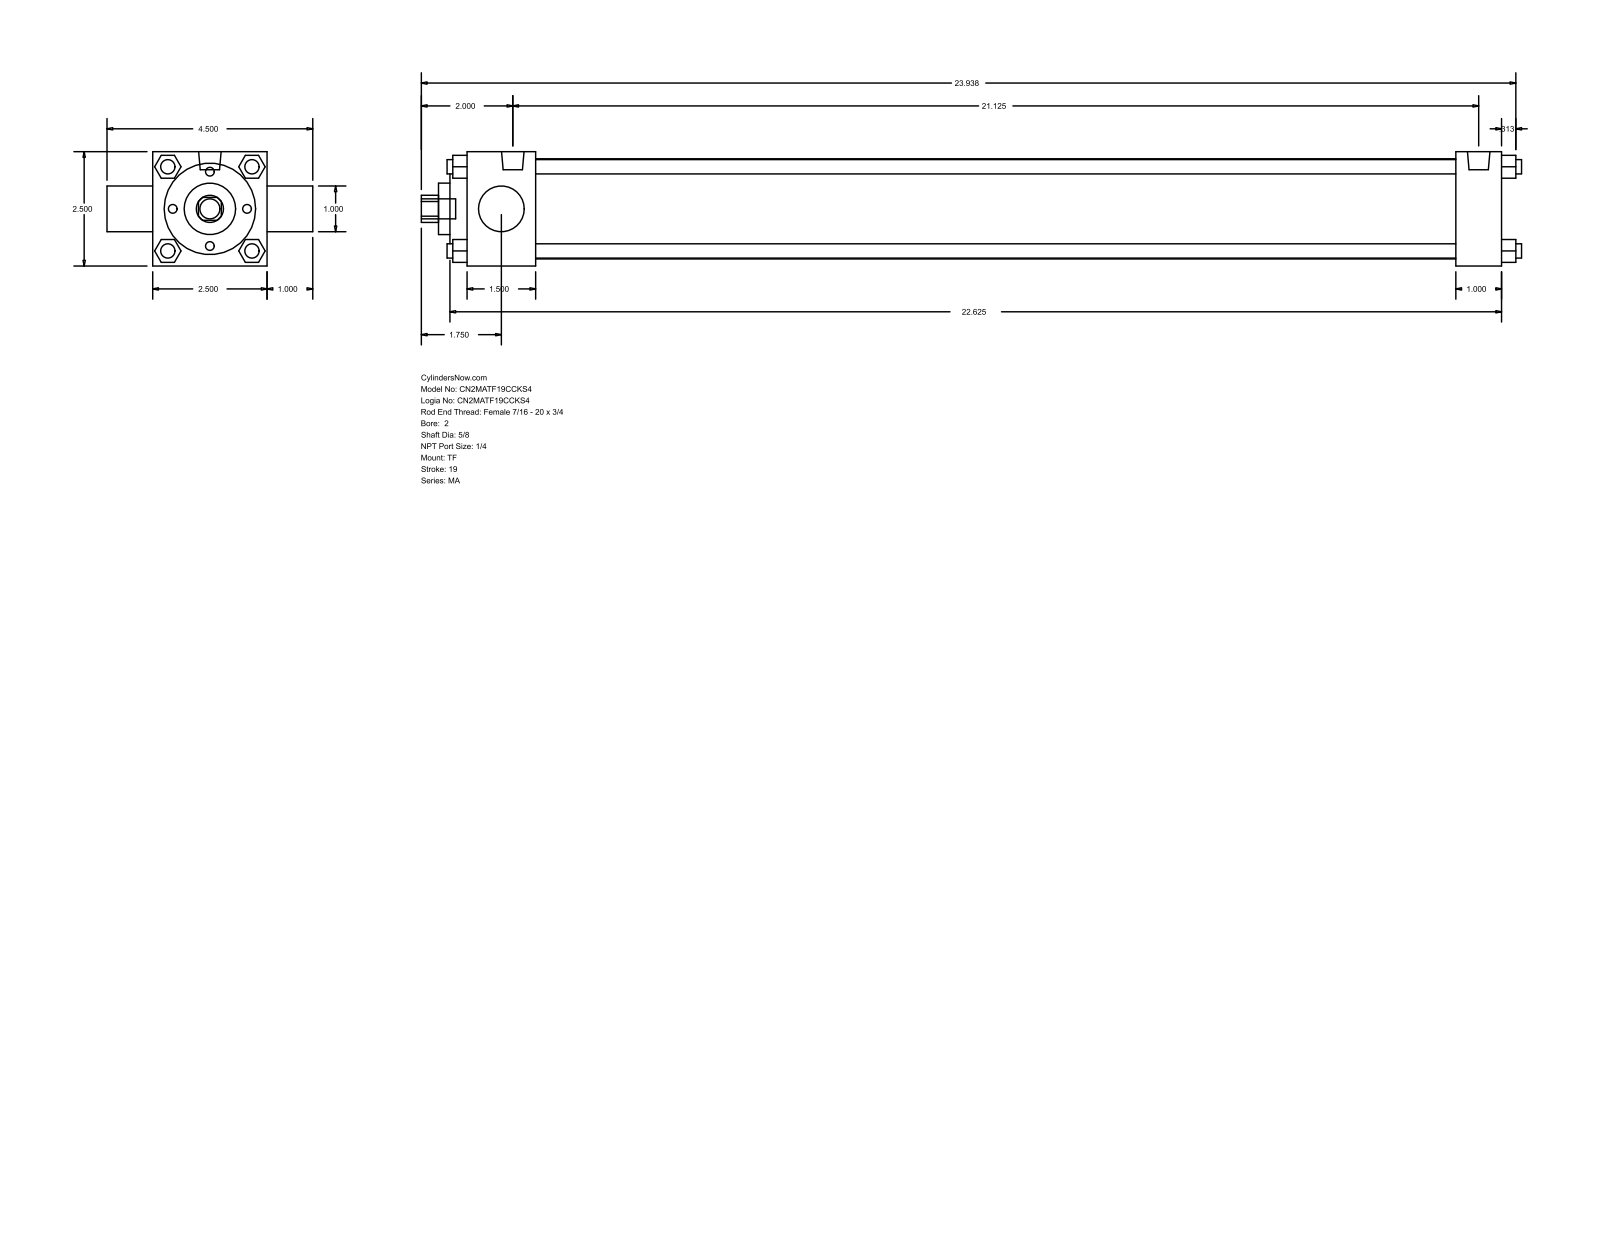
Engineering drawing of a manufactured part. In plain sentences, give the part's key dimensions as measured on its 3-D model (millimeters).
The part is named "MA_TF__0200_0.625". Its 3-D file was written by "GSSL Pune (CONFIG_CONTROL_DESIGN)". It is 0 solids with 122 faces: 93 planar, 29 cylindrical and 0 other. Overall it measures 611.19 by 114.3 by 63.5 millimeters. Round holes: 1 of diameter 15.88, 1 of diameter 25.4, 1 of diameter 28.57, 1 of diameter 50.8, 1 of diameter 55.63. Round bosses or shafts: 7 of diameter 7.94, 2 of diameter 12.49, 1 of diameter 11.11. Partial cylindrical surfaces (rounded edges, fillets, slot ends): 1 of radius 7.54. The main face-to-face distances are 63.5, 38.1, 12.7, 9.52, 574.68, 549.27, 511.17, 536.58, 25.41, 47.62.
